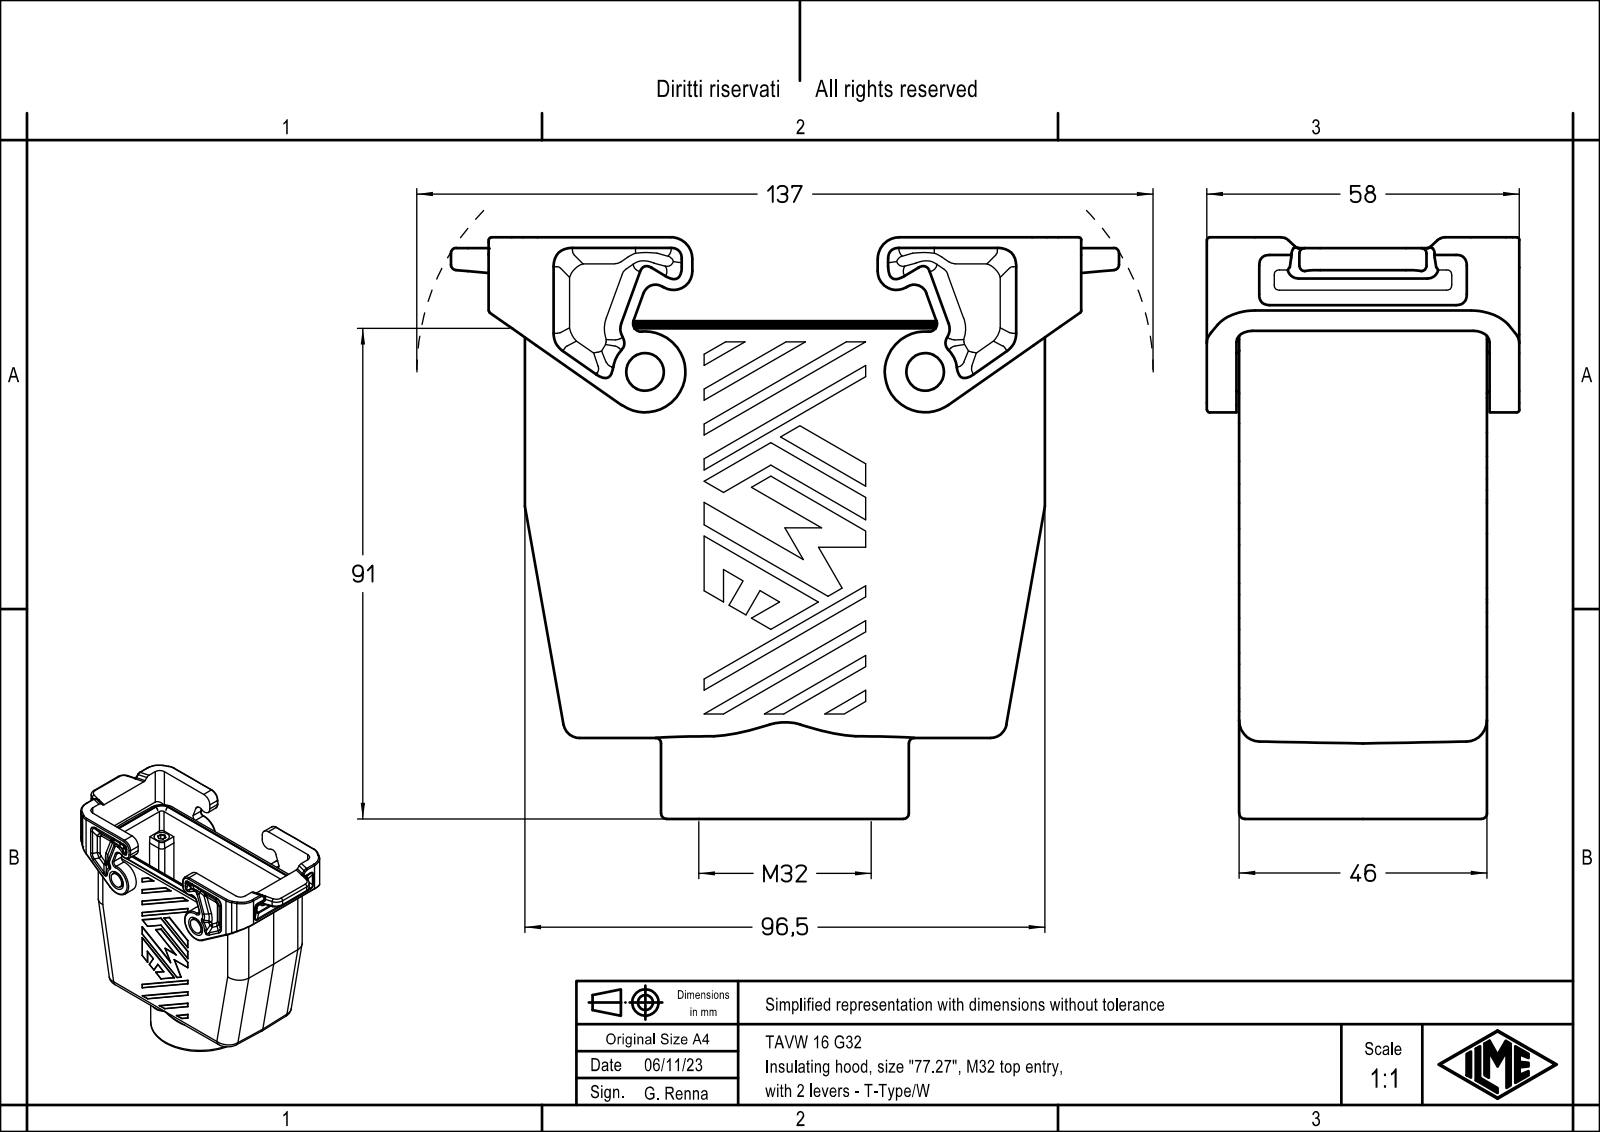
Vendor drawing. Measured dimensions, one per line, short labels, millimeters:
name: TAVW 16 G32
written by: Creo Elements/Direct Modeling 20.1B 02-Apr-2019 (C) Parametric Technology GmbH (AUTOMOTIVE_DESIGN)
unit: mm
bodies: 1 solid, 562 faces (218 planar, 282 cylindrical, 62 other)
size: 124 × 107.9 × 58
volume: 161 093 mm³; area: 60 791 mm²
holes: 1× ⌀28, 1× ⌀30.6
bosses: 2× ⌀7, 1× ⌀46
rounds: 88× R0.15, 20× R3, 16× R1, 16× R2, 10× R1.5, 8× R1.3, 8× R6, 8× R7
face distances: 5.4, 40.6, 35.2, 46, 0.5, 5.9, 41.1, 46.5, 5.5, 6
